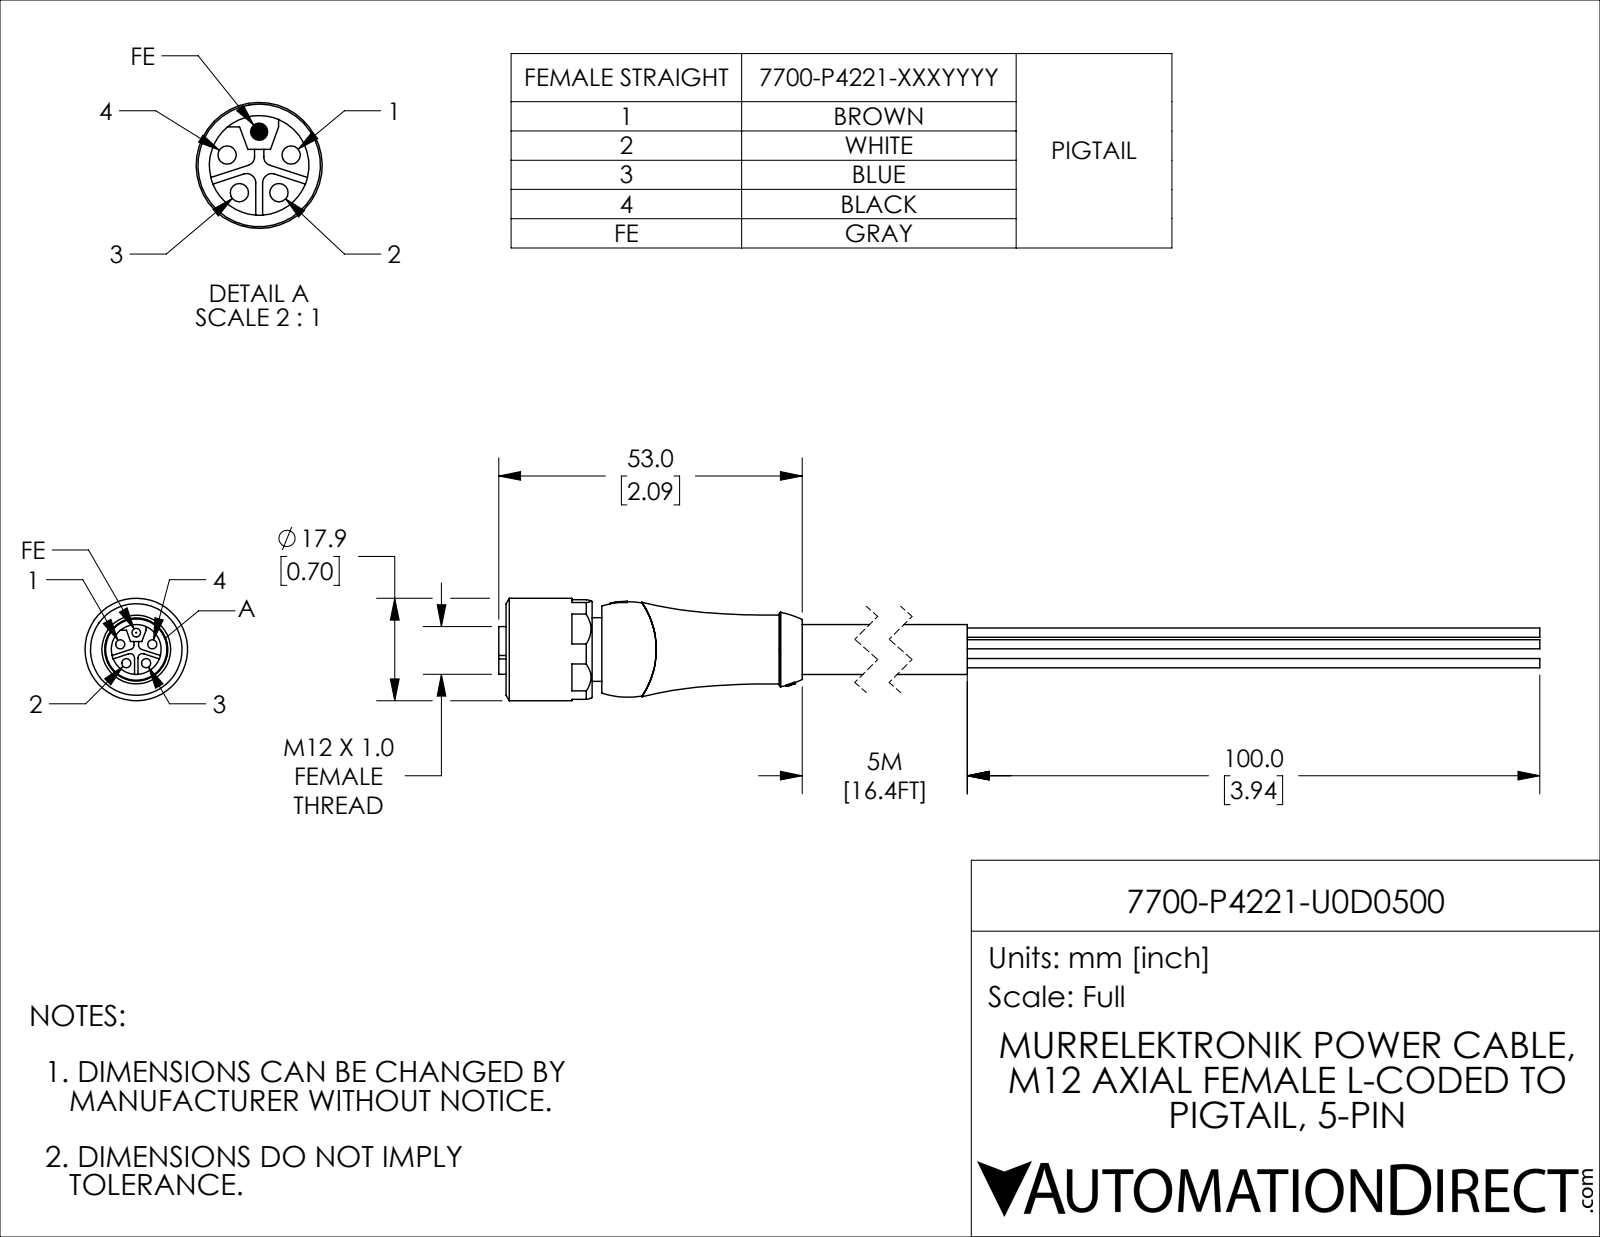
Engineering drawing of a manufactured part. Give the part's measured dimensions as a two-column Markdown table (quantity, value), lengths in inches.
| quantity | value |
| --- | --- |
| part name | 7700-P4221-U0D0500 |
| STEP written by | SolidWorks 2021 (CONFIG_CONTROL_DESIGN) |
| units | inches |
| bodies | 2 solids, 142 faces (69 planar, 40 cylindrical, 33 other) |
| overall size | 7.598 × 0.705 × 0.705 |
| volume | 0.735 in³ |
| surface area | 12.83 in² |
| round holes (diameter × count) | 0.063 × 4, 0.433 × 1, 0.512 × 1 |
| round bosses / shafts (diameter × count) | 0.705 × 1, 0.51 × 1, 0.437 × 1, 0.343 × 1, 0.063 × 1, 0.059 × 1 |
| partial cylindrical surfaces (radius × count) | 0.031 × 4 |
| main face-to-face distances | 0.657, 0.591, 0.067, 0.667, 3.61, 3.02, 2.953, 0.181, 0.362, 0.228 |
| hole center spacings | 0.116, 0.136, 0.22 |
